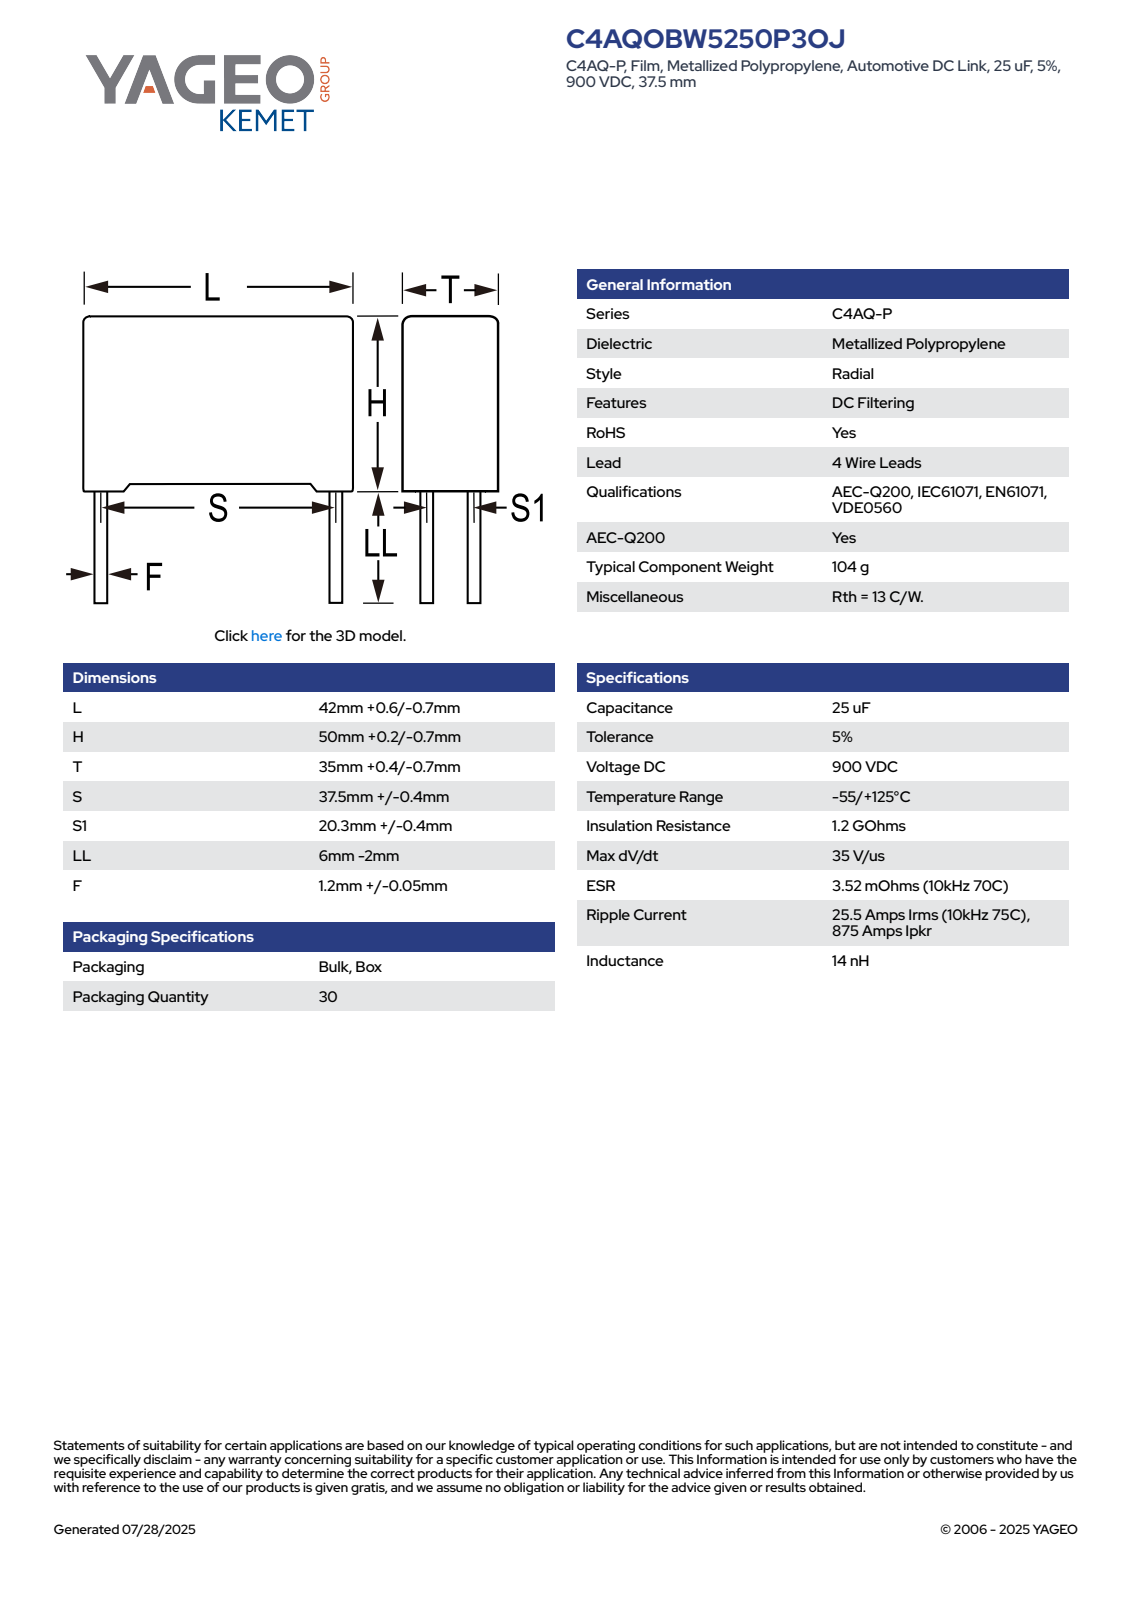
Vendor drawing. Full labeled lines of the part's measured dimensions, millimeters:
Part name (STEP PRODUCT): CFP_RB4_42X50X35_L42.6H50.2T35.4S37.5S120.3LL4F1.25
STEP written by: SolidWorks 2014 (AUTOMOTIVE_DESIGN)
Units: millimetres
Bodies: 4 solids, 91 faces (83 planar, 8 cylindrical, 0 other)
Overall size (bounding box): 54.2 × 42.6 × 35.41
Volume: 73 799 mm³ · Surface area: 11 086 mm²
Round bosses / shafts (diameter × count): ⌀1.25 ×4
Main face-to-face distances: 35.4, 42.6, 48.72, 1.48, 50.2, 2.18, 40.42, 35.41, 38.24, 33.22
